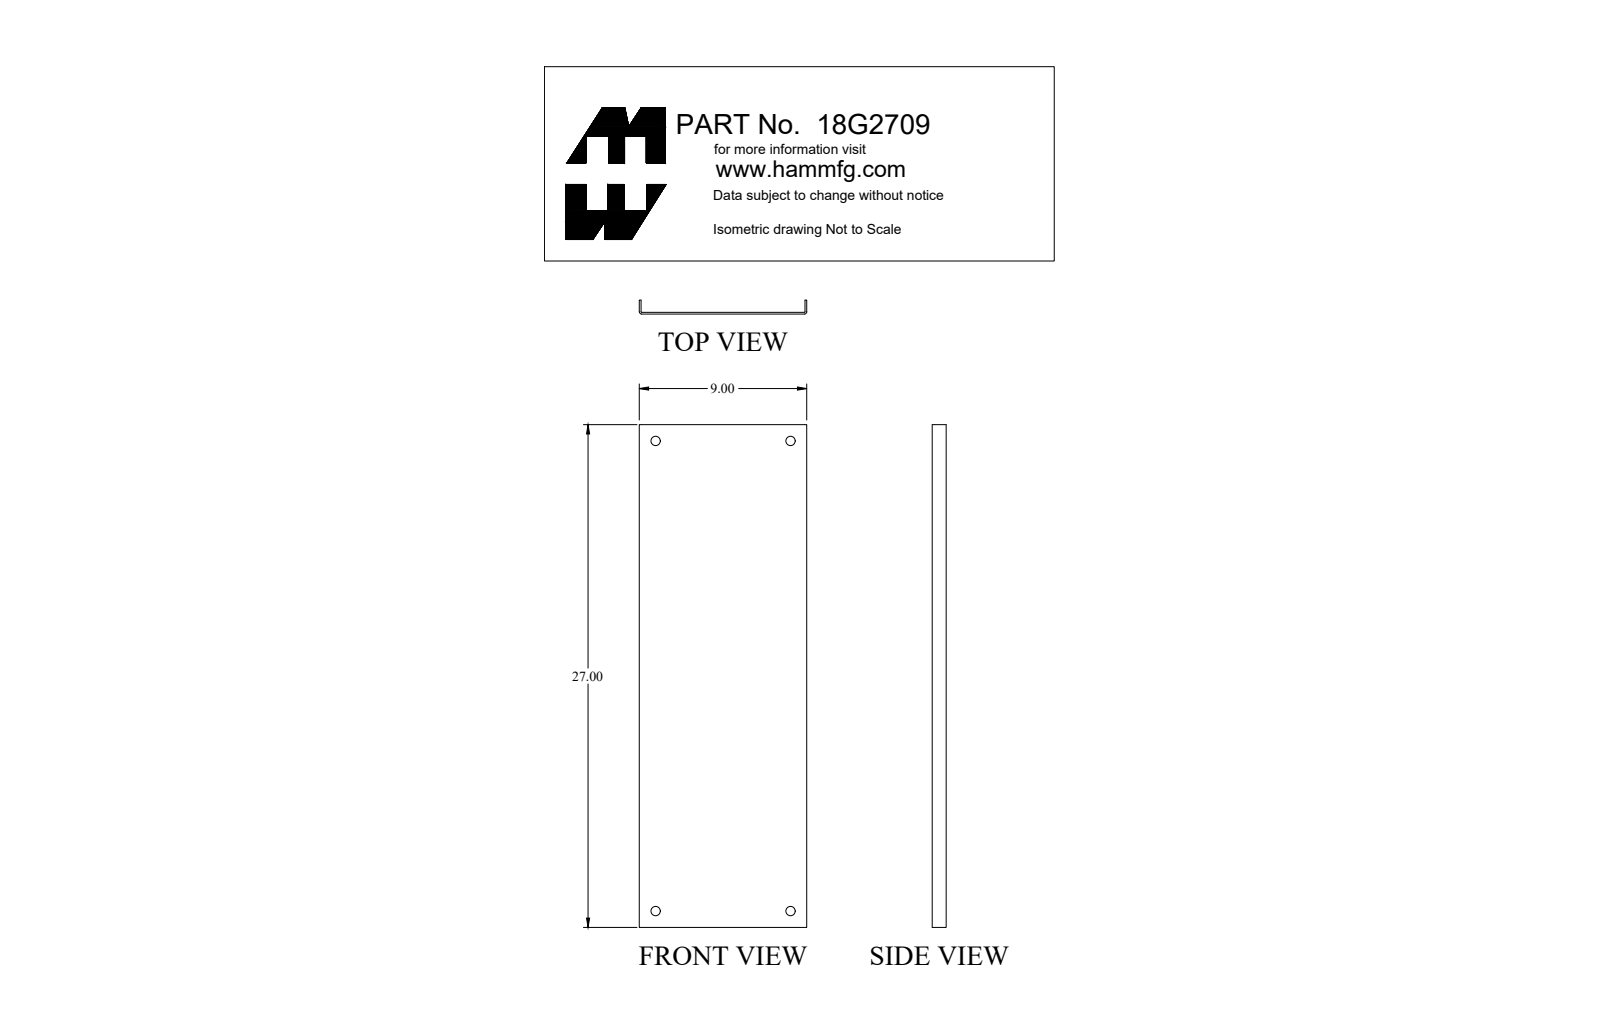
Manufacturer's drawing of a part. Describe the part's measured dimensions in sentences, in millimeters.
The part is named "18G2709". Its 3-D file was written by "SolidWorks 2018 (AUTOMOTIVE_DESIGN)". It is 1 solid with 18 faces: 10 planar, 8 cylindrical and 0 other. Overall it measures 685.8 by 228.6 by 19.1 millimeters. Its volume is 429 300 cubic millimeters and its surface area 360 800 square millimeters. Round holes: 4 of diameter 12.7. Partial cylindrical surfaces (rounded edges, fillets, slot ends): 2 of radius 0.8, 2 of radius 3.2. The main face-to-face distances are 2.4, 226.2, 228.6, 223.8, 19.1, 16.6, 685.8. The hole center spacings are 184.2, 641.4, 667.3.
